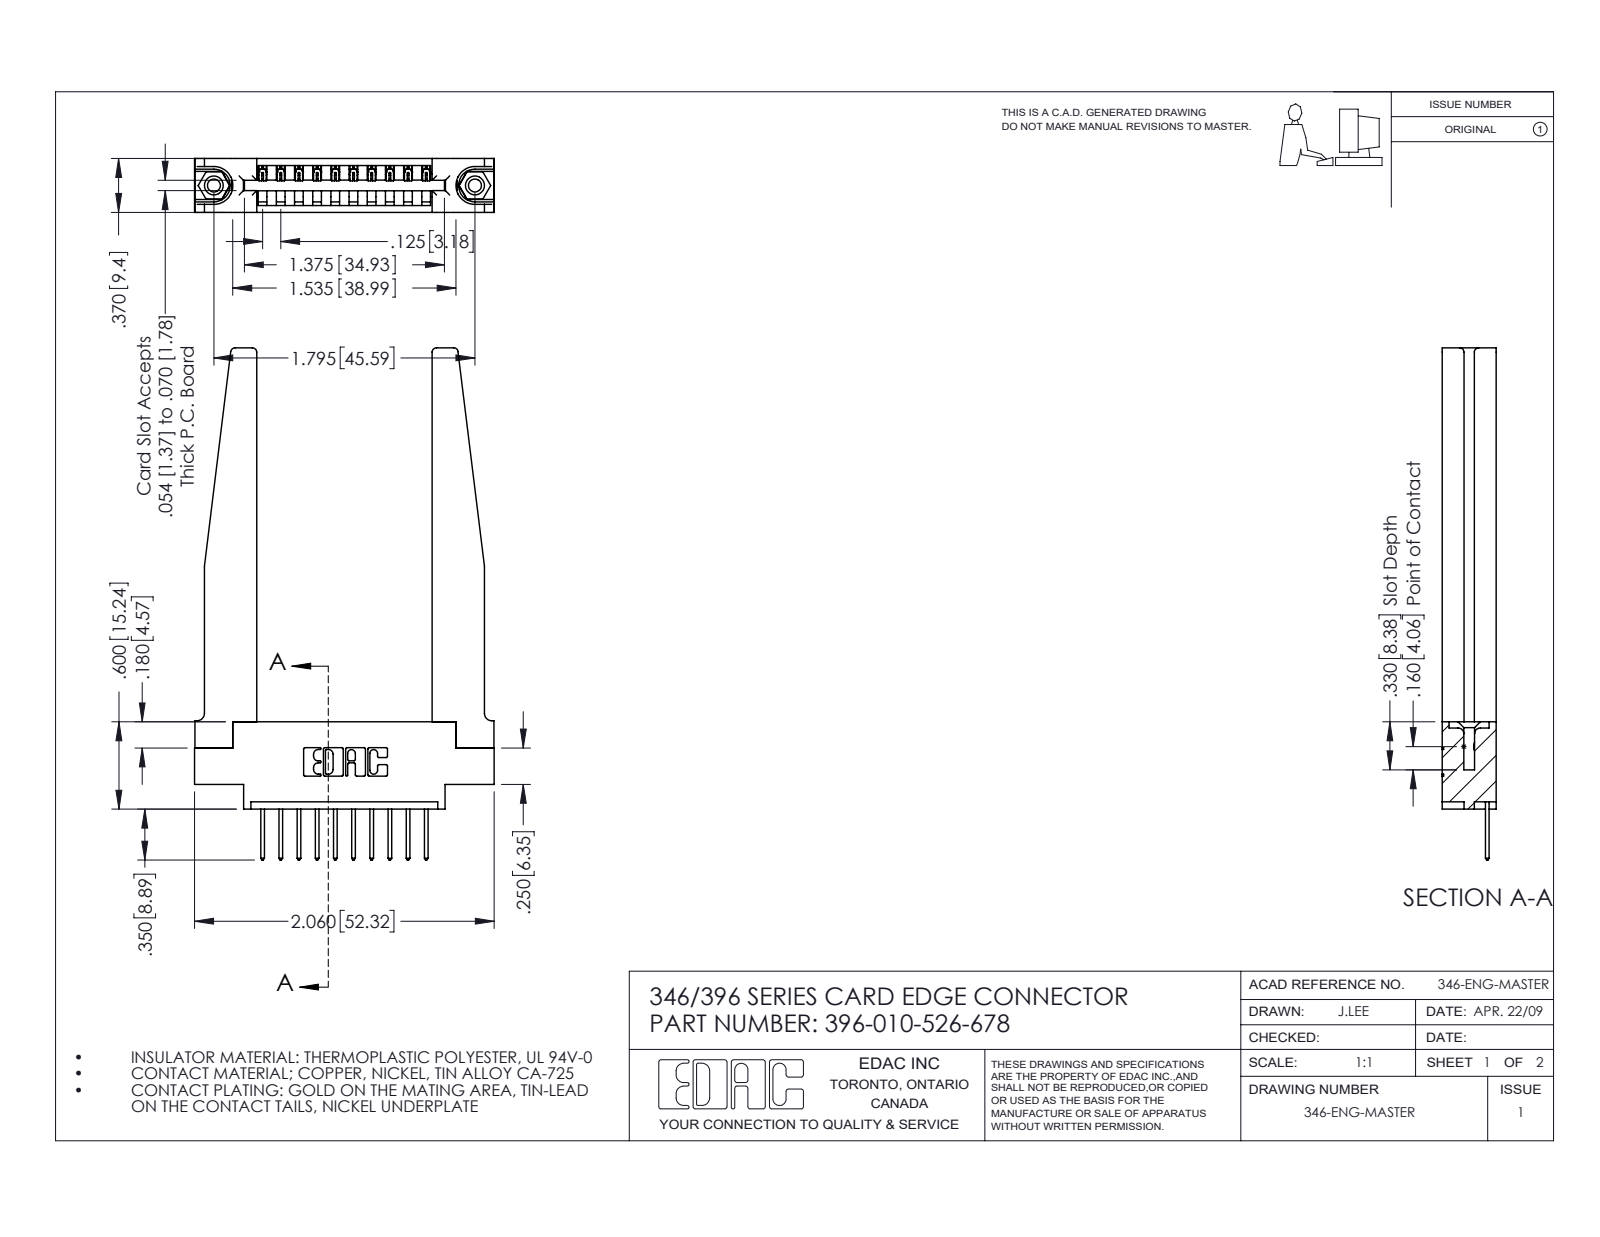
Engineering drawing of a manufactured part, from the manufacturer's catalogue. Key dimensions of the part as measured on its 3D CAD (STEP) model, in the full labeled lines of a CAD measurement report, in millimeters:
Part name (STEP PRODUCT): 345-292-001_345-293-126; 346 Part_0.170 Offset - 0.156 Dia-TH; 346-220-078_345-220-078; 345-250-001_345-250-001-102 (+1 more)
STEP written by: SolidWorks 2016 (CONFIG_CONTROL_DESIGN)
Units: millimetres
Bodies: 15 solids, 940 faces (622 planar, 266 cylindrical, 52 other)
Overall size (bounding box): 89.4 × 52.3 × 9.4
Volume: 11 500 mm³ · Surface area: 12 130 mm²
Round holes (diameter × count): ⌀2.3 ×2, ⌀3.2 ×2, ⌀4 ×2, ⌀1.6 ×1
Round bosses / shafts (diameter × count): ⌀3.9 ×2
Partial cylindrical surfaces — rounded edges, fillets, slot ends (radius × count): R0.3 ×22, R0.2 ×20, R0.3 ×20, R0.8 ×8, R0.2 ×6, R0.8 ×6, R0.7 ×3, R0.8 ×2
Main face-to-face distances: 9.4, 3.8, 1.8, 3.8, 1.2, 8.2, 6.4, 5.6, 2.6, 4.4
Hole centre spacings: 6.2, 40.4, 45.6
